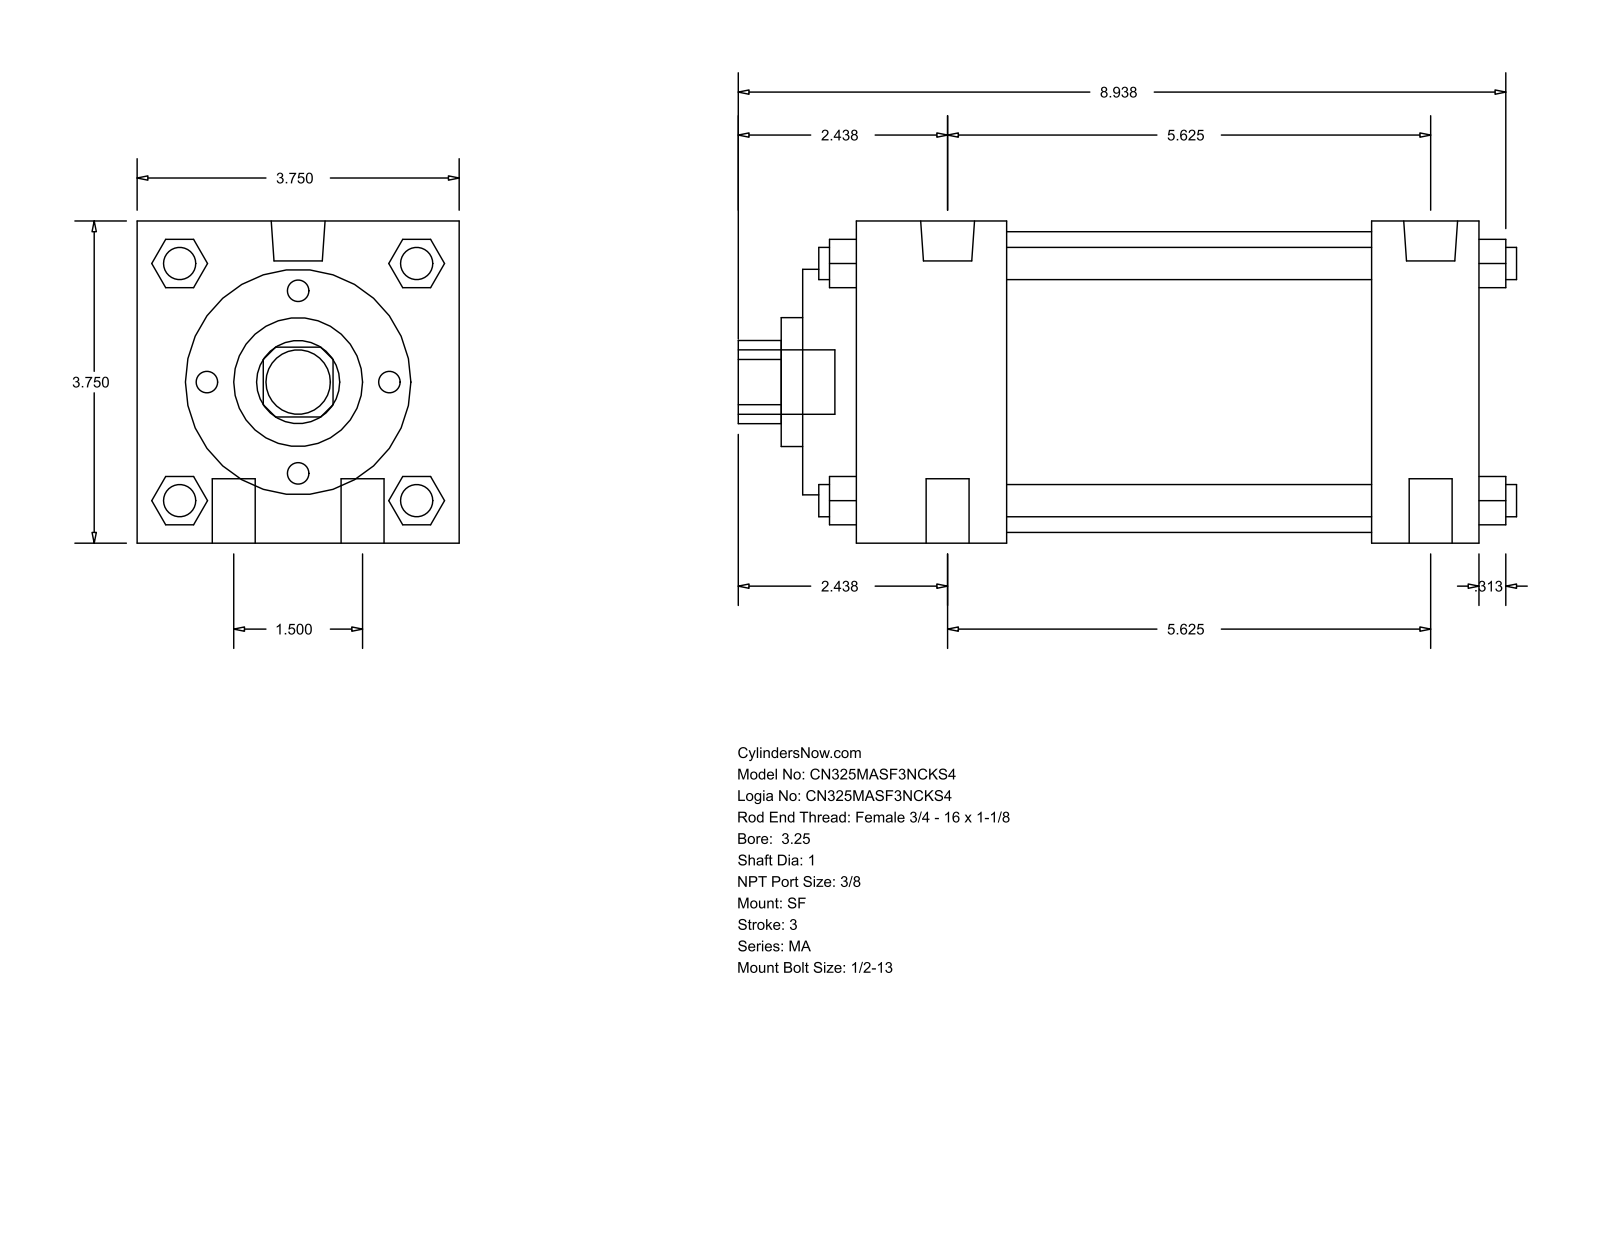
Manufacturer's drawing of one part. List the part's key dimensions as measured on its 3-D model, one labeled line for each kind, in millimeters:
Part name (STEP PRODUCT): MA_SF__0325_1
STEP written by: GSSL Pune (CONFIG_CONTROL_DESIGN)
Units: millimetres
Bodies: 0 solids, 126 faces (95 planar, 31 cylindrical, 0 other)
Overall size (bounding box): 230.19 × 95.25 × 95.25
Round holes (diameter × count): ⌀25.4 ×1, ⌀38.1 ×1, ⌀66.67 ×1, ⌀88.9 ×1
Round bosses / shafts (diameter × count): ⌀12.7 ×4, ⌀9.53 ×4, ⌀15.93 ×2, ⌀11.11 ×2, ⌀19.05 ×1
Partial cylindrical surfaces — rounded edges, fillets, slot ends (radius × count): R12.29 ×1
Main face-to-face distances: 95.24, 184.15, 200.02, 15.87, 152.4, 31.75, 44.46, 107.94, 139.69, 60.33
